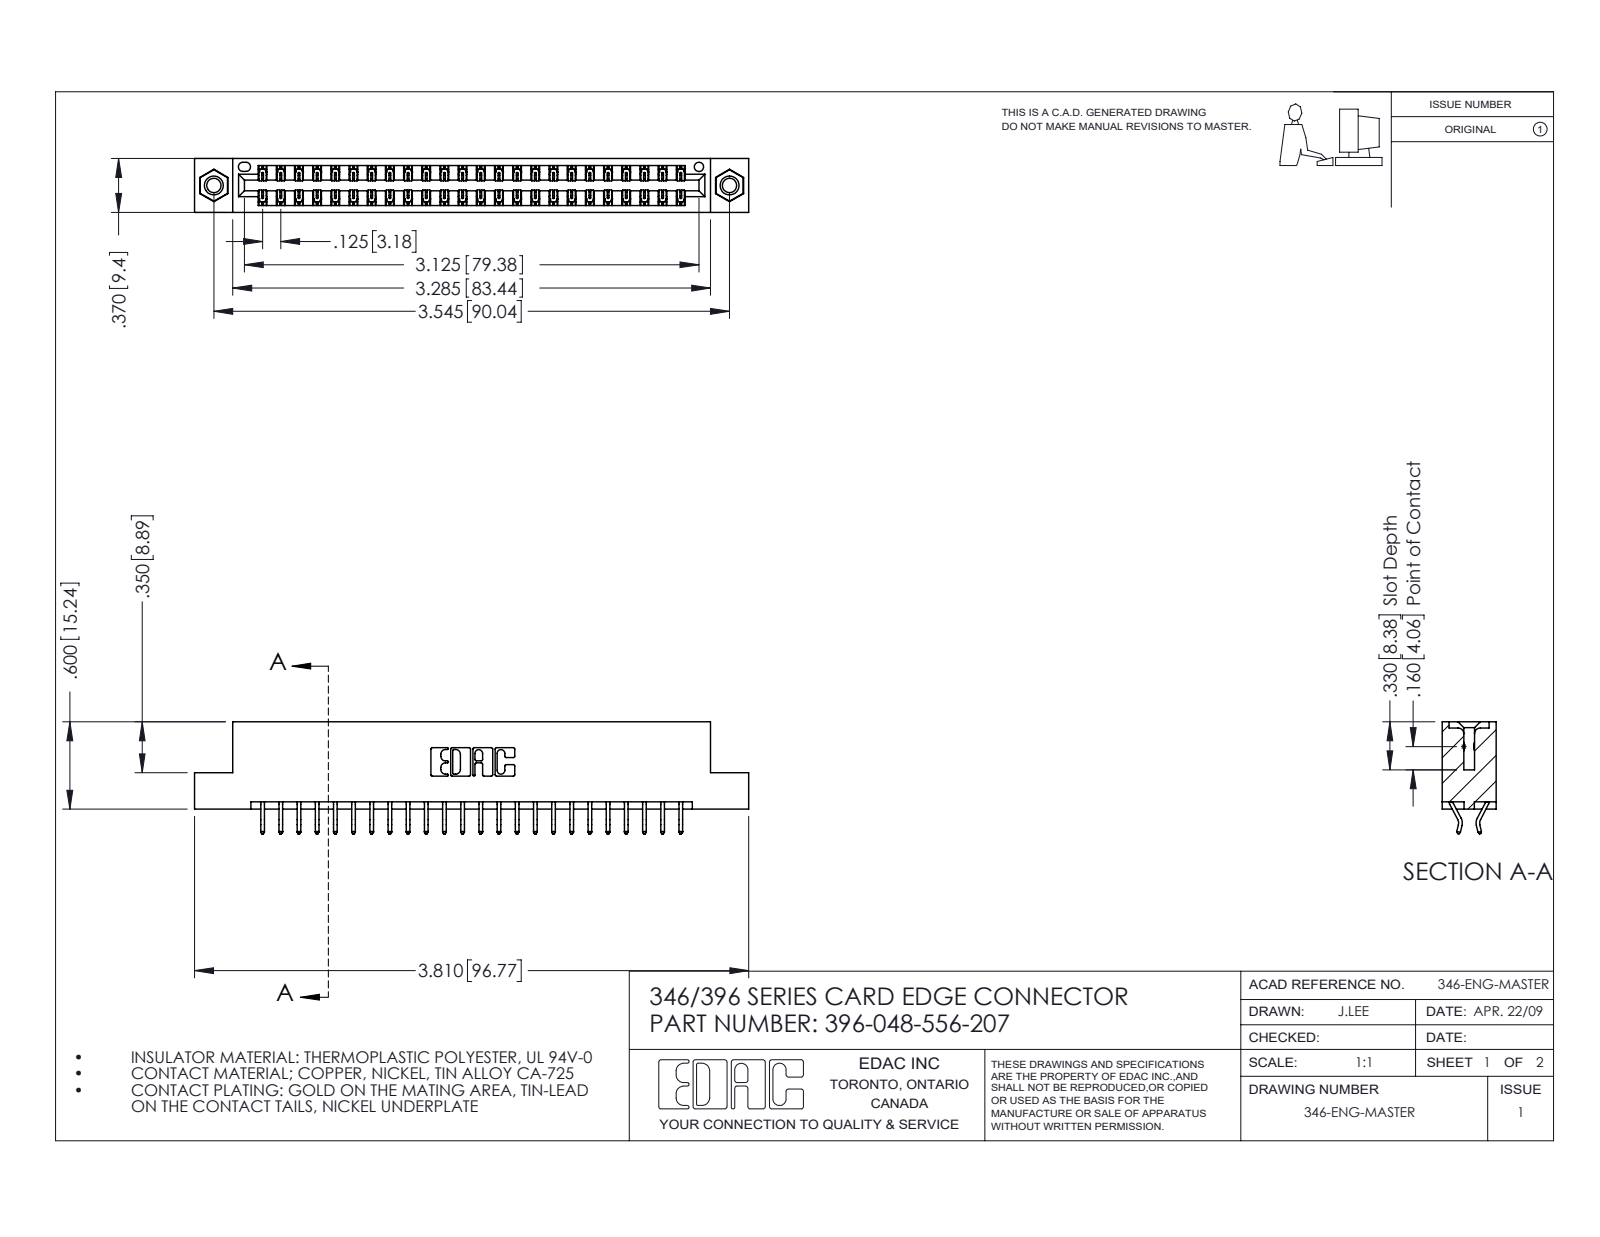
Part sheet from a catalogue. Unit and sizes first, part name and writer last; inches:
Units: inches
Overall size (bounding box): 3.81 × 0.77 × 0.37
Round holes (diameter × count): ⌀0.098 ×2, ⌀0.125 ×2, ⌀0.156 ×2, ⌀0.064 ×1
Round bosses / shafts (diameter × count): ⌀0.155 ×2
Partial cylindrical surfaces — rounded edges, fillets, slot ends (radius × count): R0.006 ×72, R0.01 ×22, R0.007 ×6, R0.031 ×6, R0.026 ×3, R0.01 ×2, R0.014 ×2, R0.022 ×2
Main face-to-face distances: 0.048, 0.322, 0.37, 0.25, 0.025, 0.072, 0.298, 0.275, 0.148, 0.222
Hole centre spacings: 0.246, 3.337, 3.545
Volume: 0.566 in³ · Surface area: 19.32 in²
Bodies: 51 solids, 2966 faces (1980 planar, 970 cylindrical, 16 other)
Part name (STEP PRODUCT): 345-292-001_556 Tail; 345-250-001_345-250-005-103; 346 Part_Flush Mounting Lugs - 0.156 Dia-TI; 396-048-556-207
STEP written by: SolidWorks 2016 (CONFIG_CONTROL_DESIGN)
